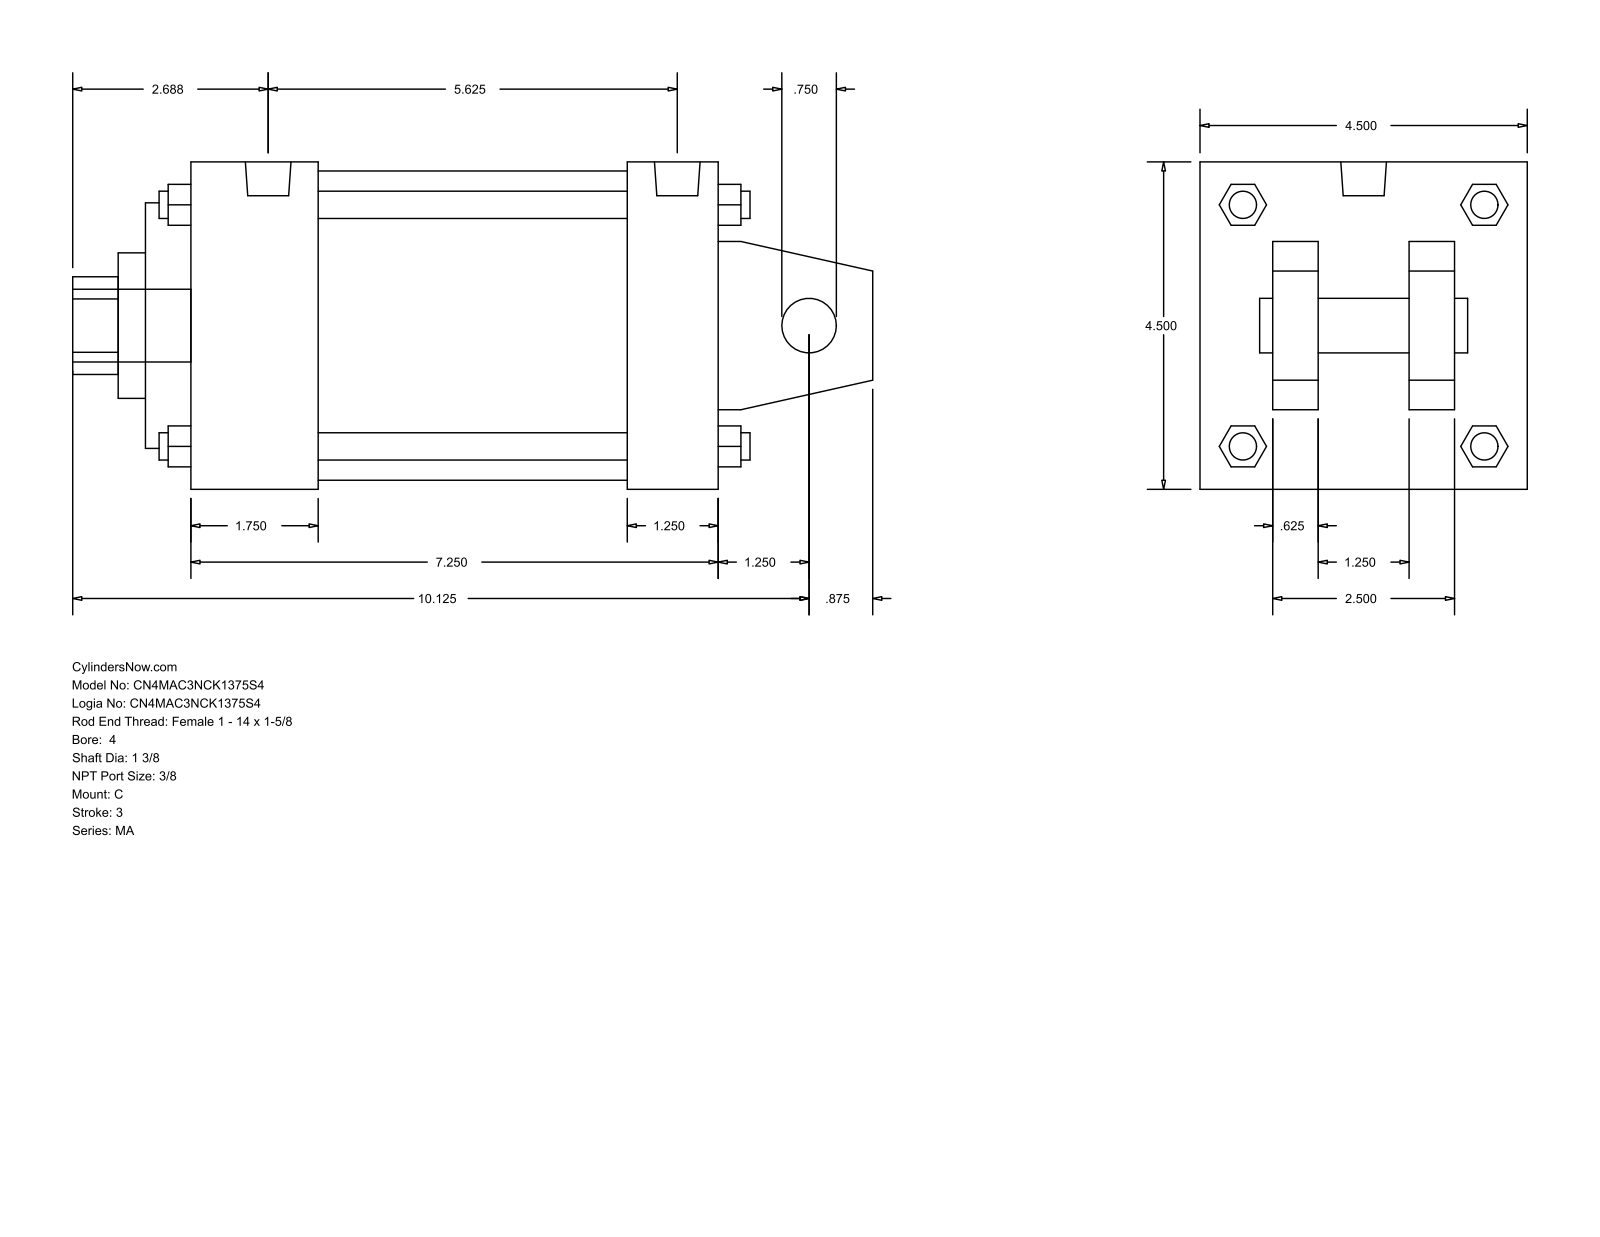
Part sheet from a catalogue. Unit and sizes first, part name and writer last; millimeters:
Units: millimetres
Overall size (bounding box): 279.4 × 114.3 × 114.3
Round holes (diameter × count): ⌀19.05 ×1, ⌀34.92 ×1, ⌀50.8 ×1, ⌀85.72 ×1, ⌀107.95 ×1
Round bosses / shafts (diameter × count): ⌀11.11 ×4, ⌀9.53 ×4, ⌀15.93 ×2, ⌀25.4 ×1
Partial cylindrical surfaces — rounded edges, fillets, slot ends (radius × count): R17.06 ×1
Main face-to-face distances: 114.3, 15.87, 184.16, 73.03, 41.27, 25.4, 88.9, 47.63, 200.03, 168.28
Bodies: 0 solids, 141 faces (109 planar, 32 cylindrical, 0 other)
Part name (STEP PRODUCT): MA_C__0400_1.375
STEP written by: GSSL Pune (CONFIG_CONTROL_DESIGN)
